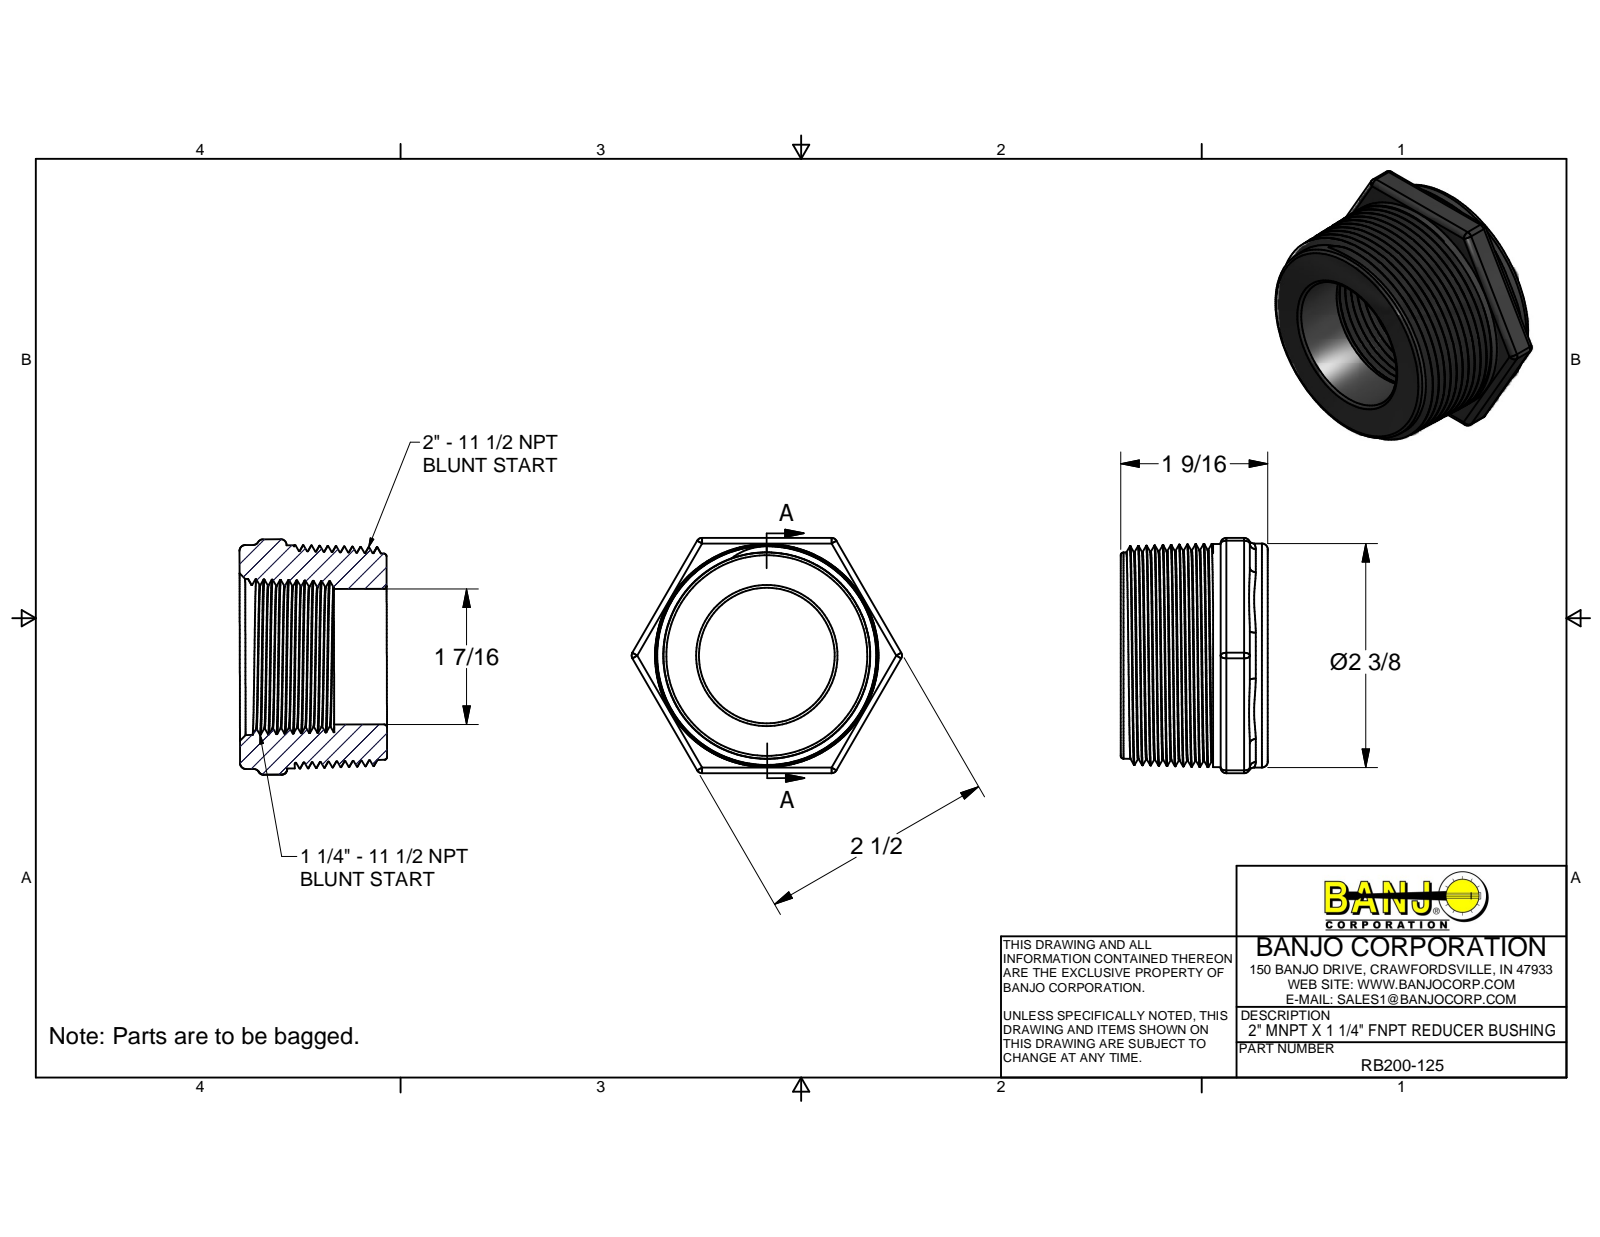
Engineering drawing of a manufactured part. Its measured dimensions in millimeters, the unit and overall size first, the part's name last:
Units: millimetres
Overall size (bounding box): 72.85 × 63.5 × 39.62
Round holes (diameter × count): ⌀36.58 ×1
Round bosses / shafts (diameter × count): ⌀60.45 ×1, ⌀60.2 ×1
Partial cylindrical surfaces — rounded edges, fillets, slot ends (radius × count): R1.52 ×18, R12.16 ×1, R15.56 ×1
Main face-to-face distances: 39.62, 63.5, 12.7, 26.92, 25.4, 14.22, 14.73, 2.03, 10.67, 24.89
Volume: 64 964 mm³ · Surface area: 21 784 mm²
Bodies: 1 solid, 102 faces (17 planar, 25 cylindrical, 60 other)
Part name (STEP PRODUCT): RB200-125
STEP written by: Autodesk Inventor 2014 (AUTOMOTIVE_DESIGN)
